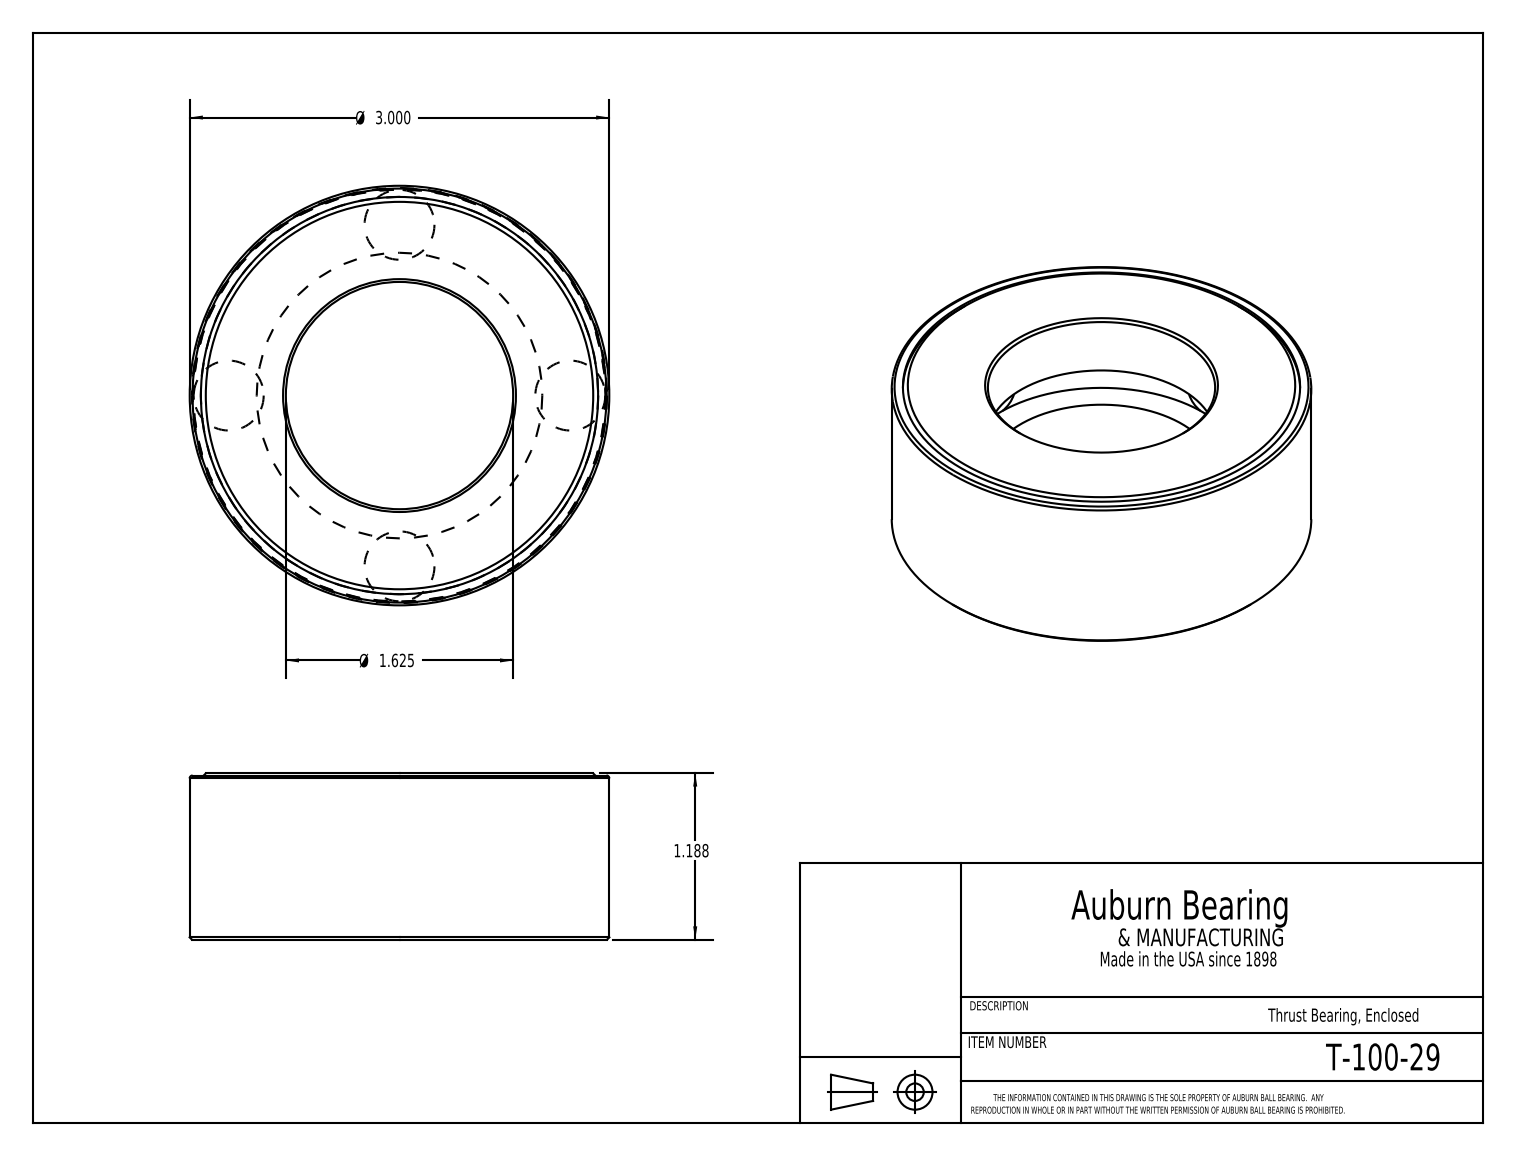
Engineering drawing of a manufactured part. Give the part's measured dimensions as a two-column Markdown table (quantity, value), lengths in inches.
| quantity | value |
| --- | --- |
| part name | T-100-29 |
| STEP written by | SolidWorks 2016 (CONFIG_CONTROL_DESIGN) |
| units | inches |
| bodies | 6 solids, 28 faces (9 planar, 7 cylindrical, 12 other) |
| overall size | 3 × 3 × 1.188 |
| volume | 4.262 in³ |
| surface area | 50.44 in² |
| round holes (diameter × count) | 1.625 × 1, 2.84 × 1, 2.96 × 1 |
| round bosses / shafts (diameter × count) | 3 × 1, 2.946 × 1 |
| main face-to-face distances | 1.187, 0.444, 0.744, 0.3, 1.172, 0.729, 0.429, 0.015, 1.152, 0.709 |
